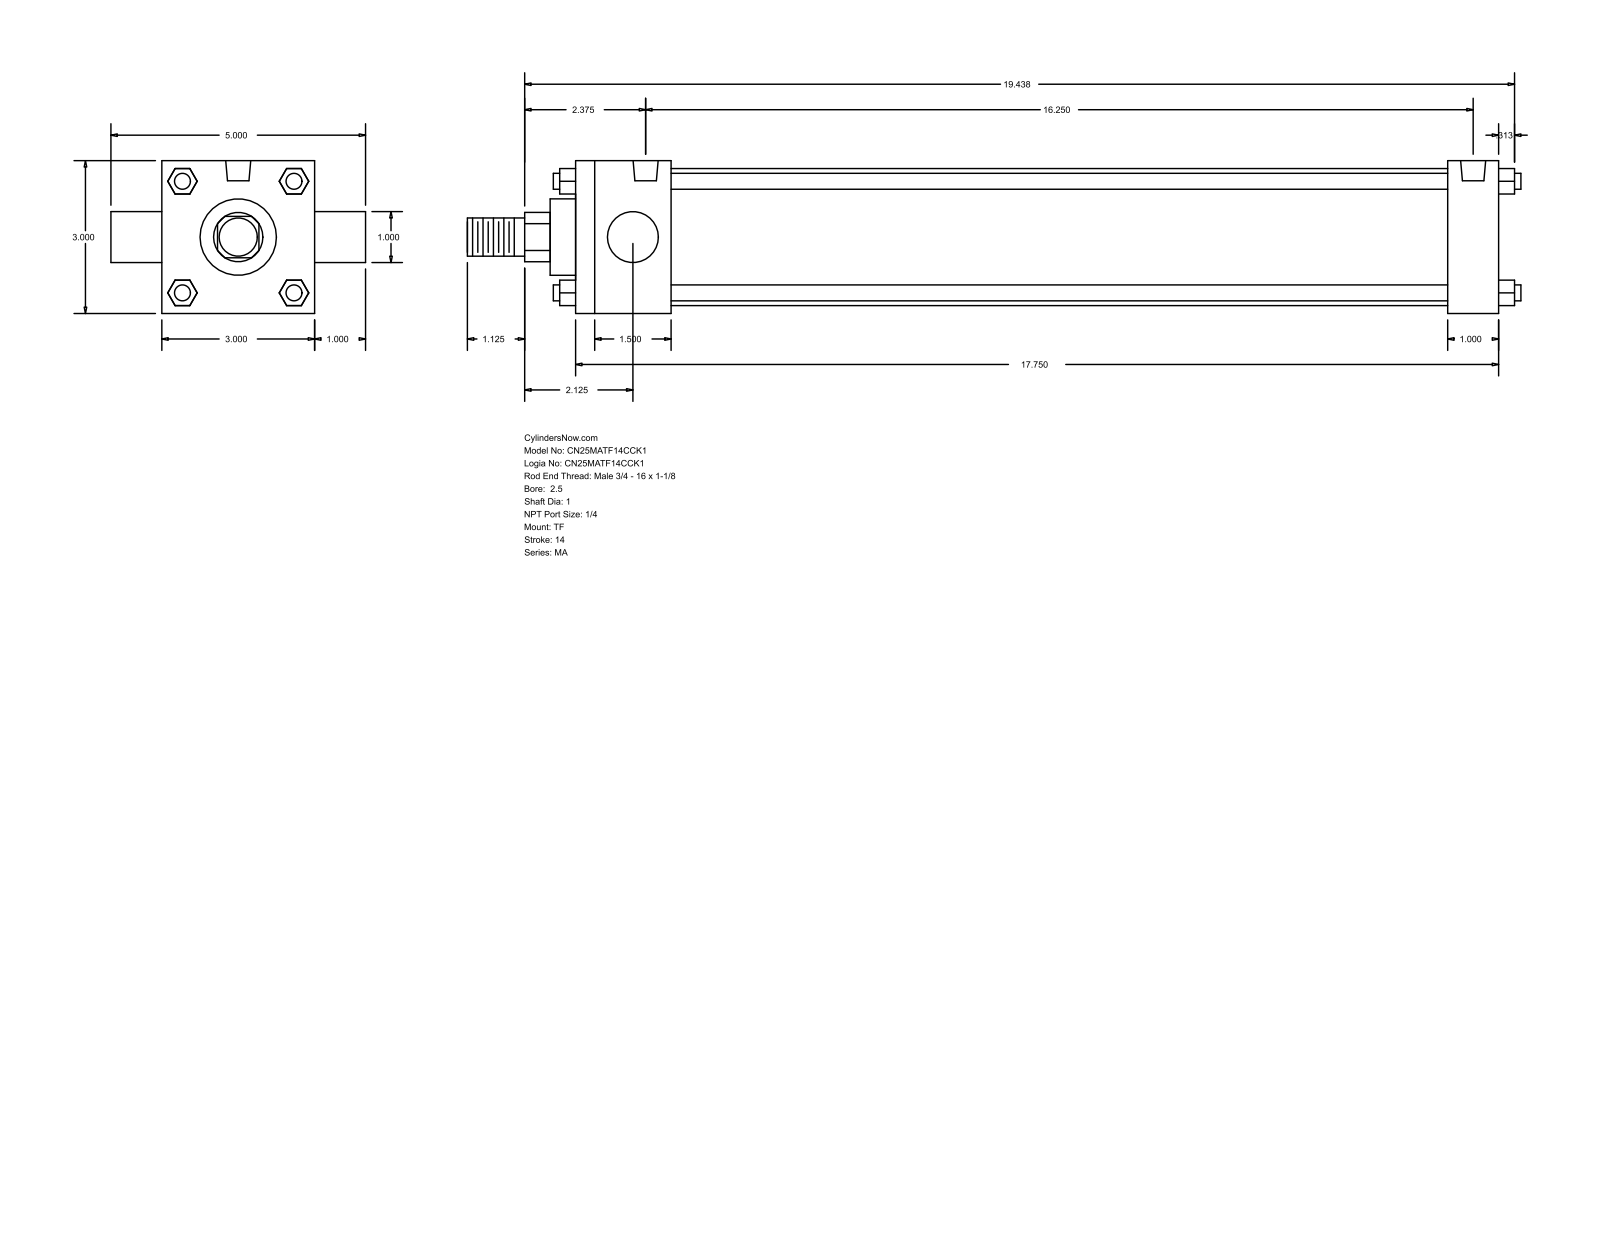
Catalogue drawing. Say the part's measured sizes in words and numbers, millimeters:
The part is named "MA_TF__0250_1". Its 3-D file was written by "GSSL Pune (CONFIG_CONTROL_DESIGN)". It is 0 solids with 120 faces: 92 planar, 28 cylindrical and 0 other. Overall it measures 525.46 by 127 by 76.2 millimeters. Round holes: 3 of diameter 7.94, 2 of diameter 12.49. Round bosses or shafts: 4 of diameter 7.94, 2 of diameter 25.4, 1 of diameter 68.33, 1 of diameter 38.1, 1 of diameter 19.05. Partial cylindrical surfaces (rounded edges, fillets, slot ends): 1 of radius 12.29. The main face-to-face distances are 76.2, 460.37, 12.7, 47.63, 434.98, 387.35, 412.74, 25.39, 101.6, 25.4. The hole center spacings are 412.74.
